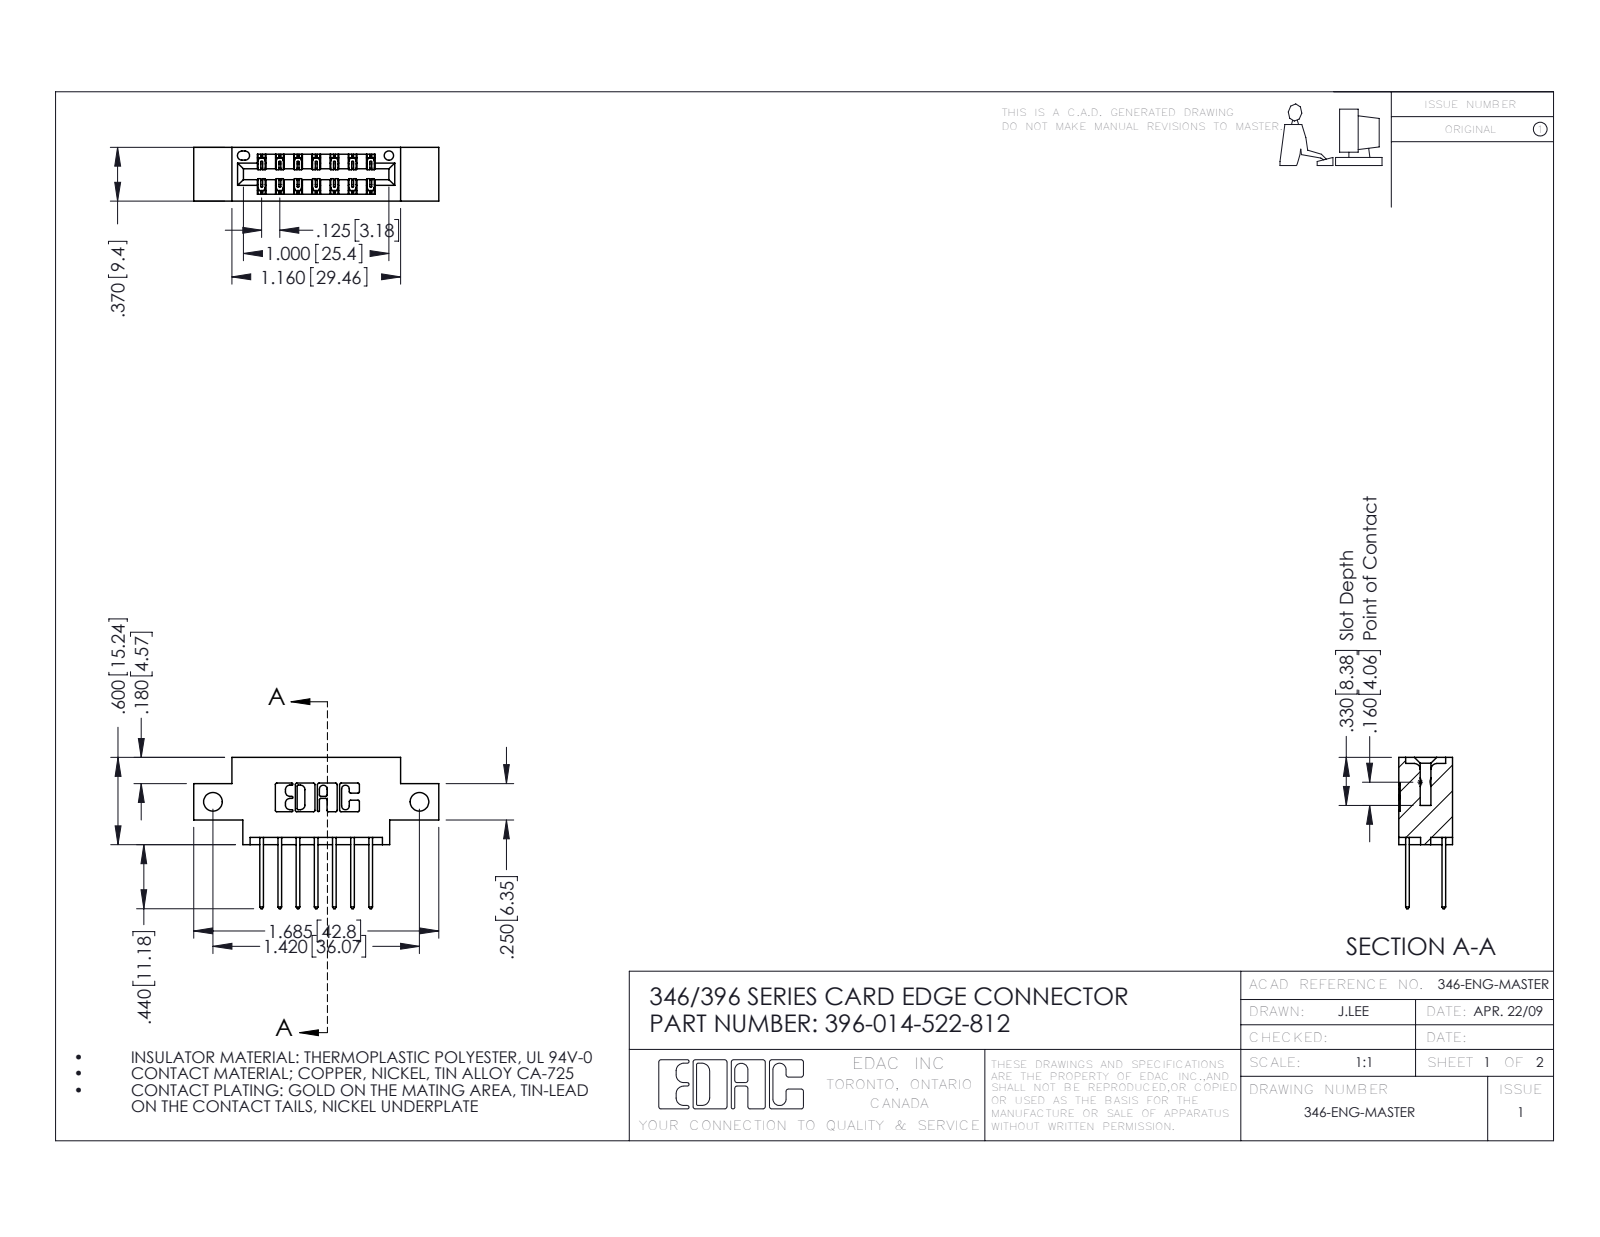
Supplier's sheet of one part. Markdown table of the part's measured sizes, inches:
| quantity | value |
| --- | --- |
| part name | 346 Part_0.170 Offset - Side Mount; 396-014-522-812; 345-292-001_345-293-122 |
| STEP written by | SolidWorks 2016 (CONFIG_CONTROL_DESIGN) |
| units | inches |
| bodies | 15 solids, 854 faces (570 planar, 284 cylindrical, 0 other) |
| overall size | 1.685 × 1.04 × 0.37 |
| volume | 0.226 in³ |
| surface area | 7.344 in² |
| round holes (diameter × count) | 0.128 × 2, 0.064 × 1 |
| partial cylindrical surfaces (radius × count) | 0.01 × 22, 0.006 × 21, 0.01 × 14, 0.007 × 6, 0.031 × 6, 0.026 × 3, 0.014 × 2, 0.022 × 2 |
| main face-to-face distances | 0.25, 0.37, 0.048, 0.322, 0.072, 0.298, 0.025, 0.275, 0.225, 0.148 |
| hole center spacings | 1.42 |
